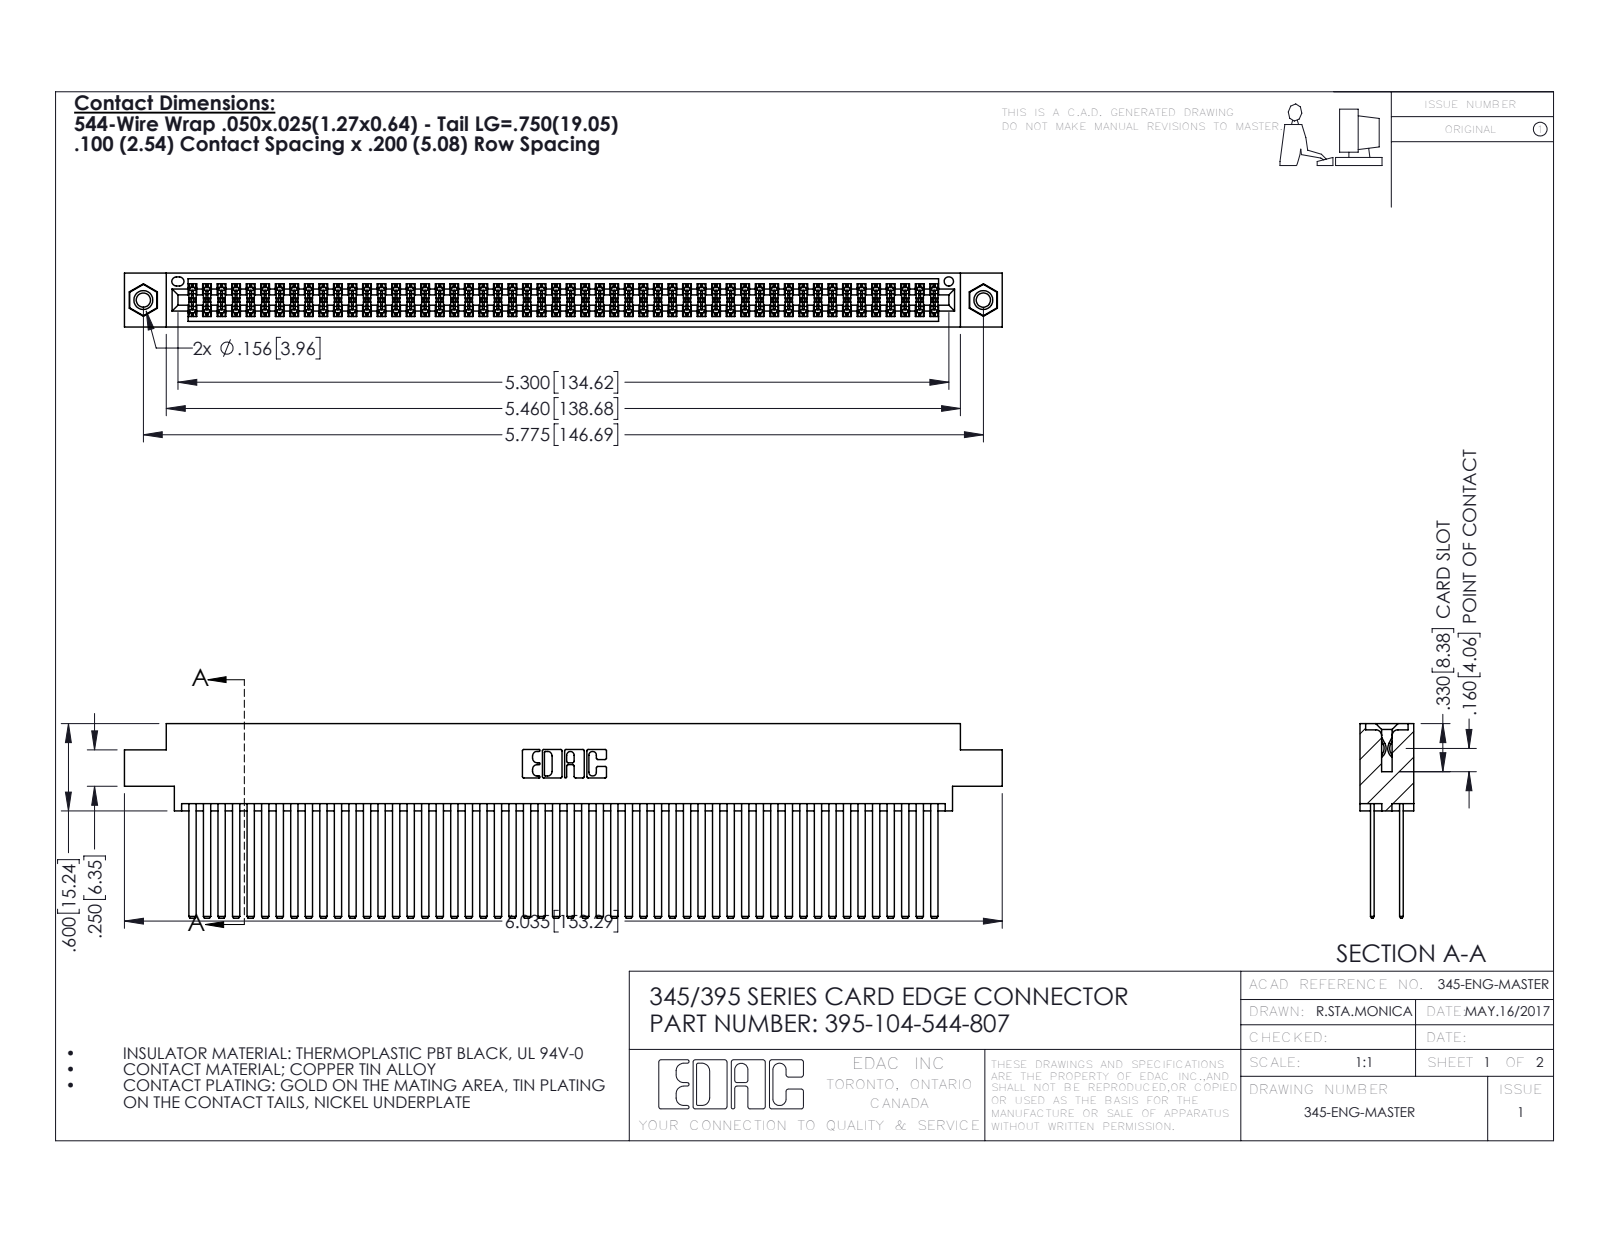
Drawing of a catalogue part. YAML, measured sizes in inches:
part_name: "345 Part_0.170 Offset - 0.156 Dia-TI; 345-292-001_345-293-144; 345-250-001_345-250-005-103; 395-104-544-807"
step_written_by: "SolidWorks 2016 (CONFIG_CONTROL_DESIGN)"
units: inches
bodies: {solids: 107, faces: 4766, planar: 3132, cylindrical: 1618, other: 16}
overall_size: [6.035, 1.337, 0.37]
volume: 0.996
surface_area: 44.57
round_holes:
  - {diameter: 0.098, count: 2}
  - {diameter: 0.125, count: 2}
  - {diameter: 0.156, count: 2}
  - {diameter: 0.064, count: 1}
round_bosses_or_shafts:
  - {diameter: 0.155, count: 2}
partial_cylinders:
  - {radius: 0.006, count: 156}
  - {radius: 0.01, count: 22}
  - {radius: 0.007, count: 6}
  - {radius: 0.031, count: 6}
  - {radius: 0.026, count: 3}
  - {radius: 0.014, count: 2}
  - {radius: 0.019, count: 2}
  - {radius: 0.022, count: 2}
face_to_face_distances: [0.2, 0.025, 0.072, 0.098, 0.272, 0.298, 0.225, 0.175, 0.37, 0.15]
hole_center_spacings: [0.27, 5.539, 5.775]
